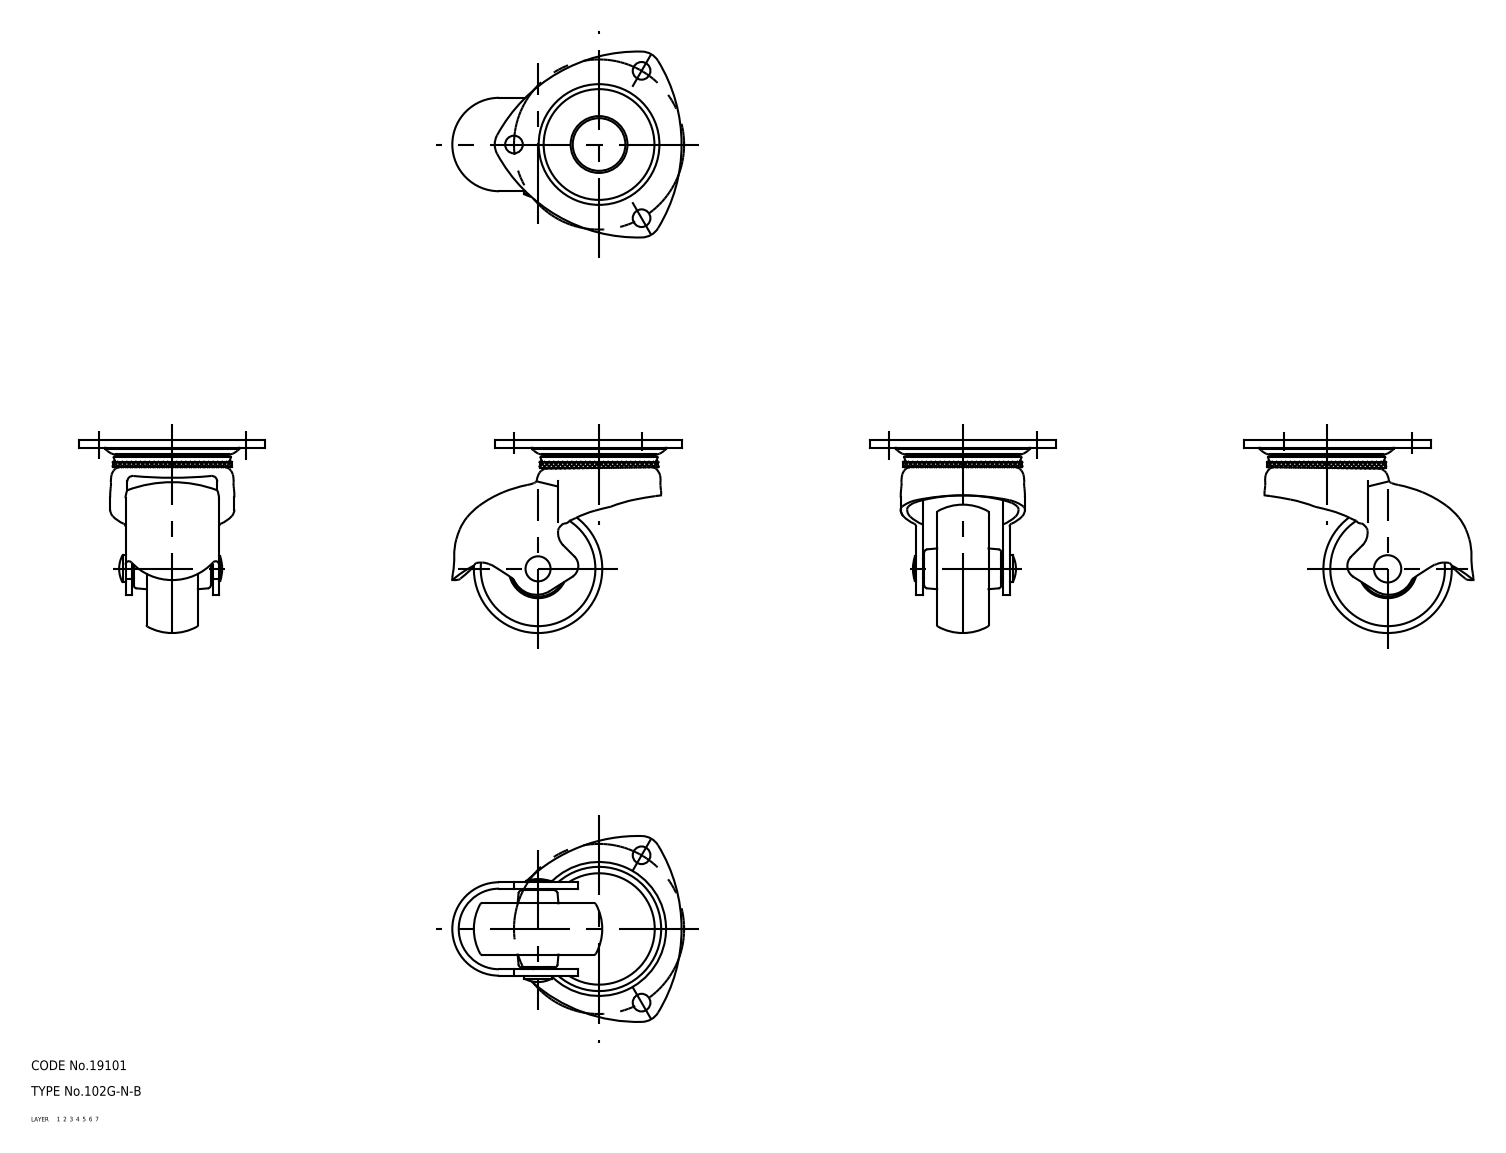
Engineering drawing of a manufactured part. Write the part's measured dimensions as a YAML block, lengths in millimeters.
part_name: "wheel; mounting plate; main shaft; axle (+1 more)"
step_written_by: "CADfix (AUTOMOTIVE_DESIGN)"
units: millimeters
bodies: {solids: 5, faces: 217, planar: 0, cylindrical: 0, other: 217}
overall_size: [71.42, 60, 57.93]
volume: 41531
surface_area: 23491
